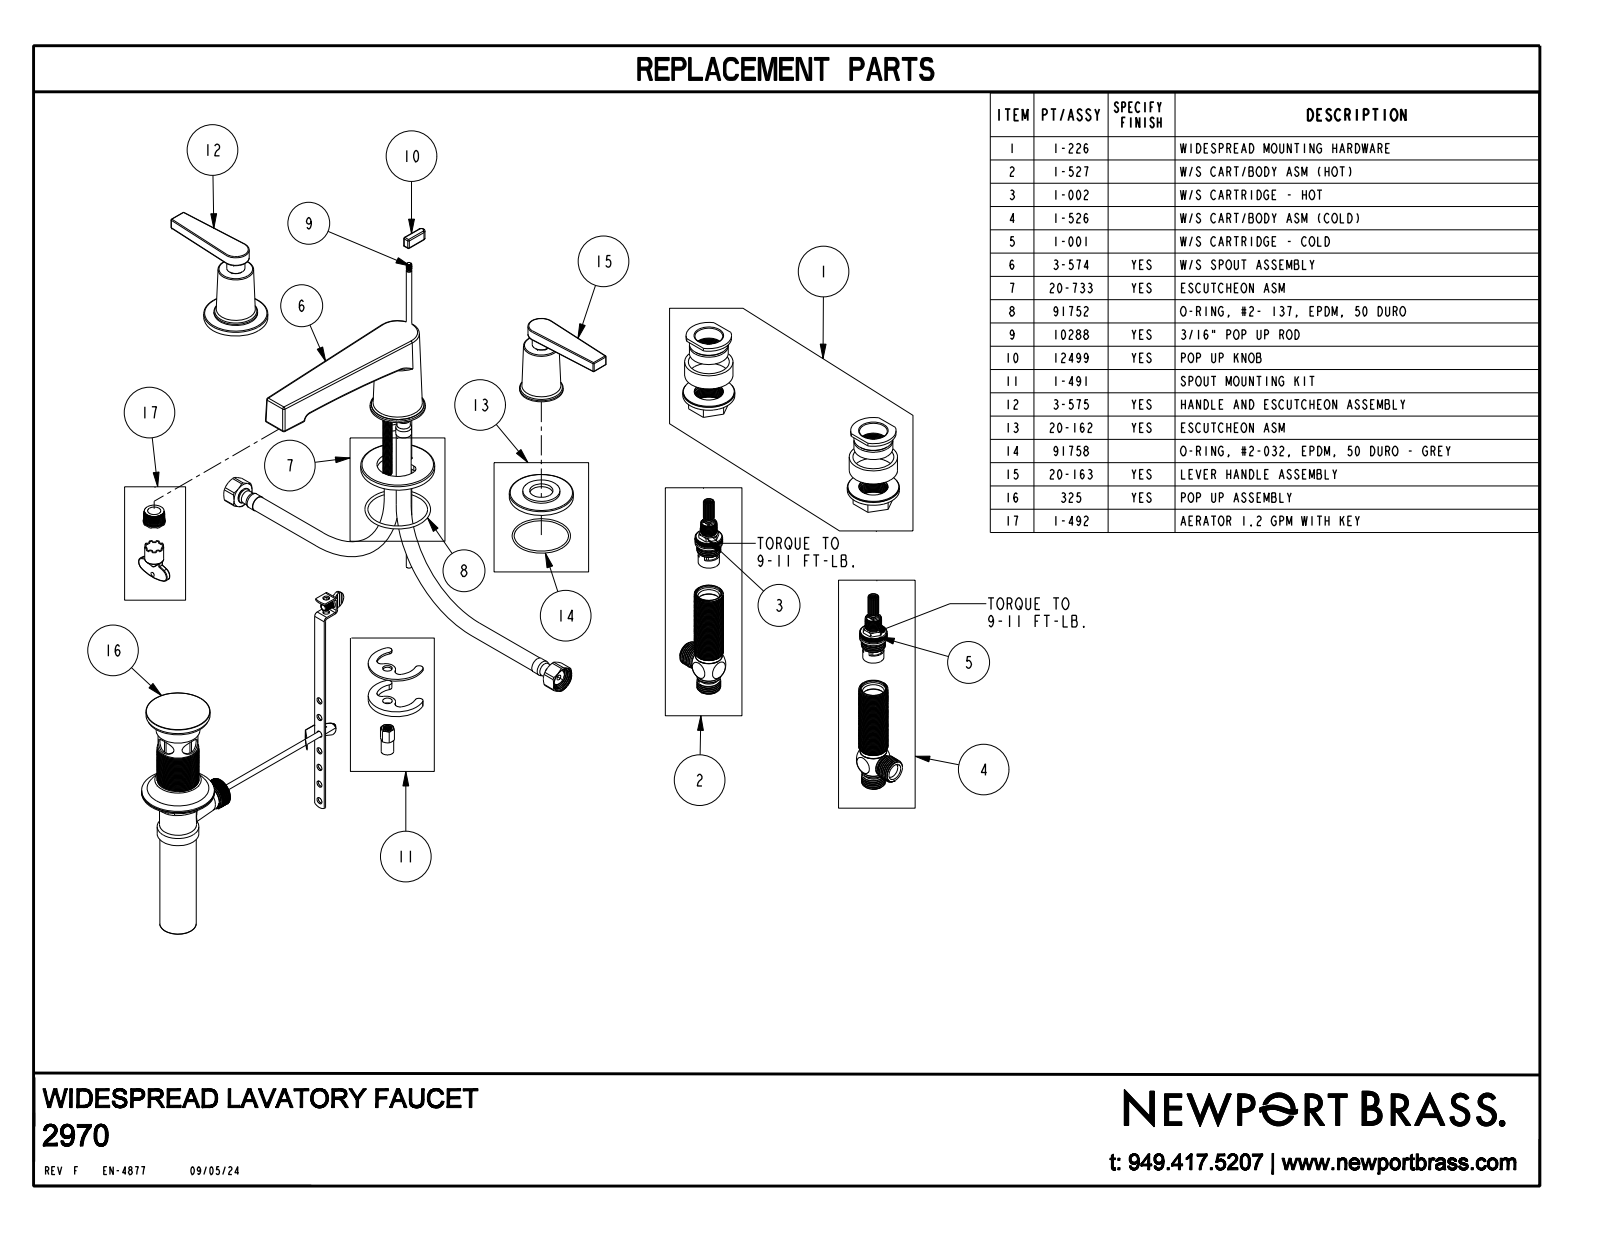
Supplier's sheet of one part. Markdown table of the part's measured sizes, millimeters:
| quantity | value |
| --- | --- |
| part name | 2970 |
| STEP written by | CREO PARAMETRIC BY PTC INC, 2018400 (CONFIG_CONTROL_DESIGN) |
| units | millimeters |
| bodies | 3 solids, 168 faces (37 planar, 67 cylindrical, 64 other) |
| overall size | 348 × 184.7 × 84.2 |
| volume | 340 400 mm³ |
| surface area | 65 610 mm² |
| round holes (diameter × count) | 33 × 2 |
| round bosses / shafts (diameter × count) | 55.9 × 2, 38.1 × 2, 32.4 × 2, 15.9 × 2, 13.3 × 2, 64.5 × 1 |
| partial cylindrical surfaces (radius × count) | 0.8 × 16, 1 × 10, 1.5 × 9, 11.7 × 2, 3.2 × 1, 4 × 1, 5.4 × 1, 889 × 1 |
| main face-to-face distances | 84.2, 4.7, 79.4, 72.9, 68.1, 11.3, 63.4, 58.6, 9.5, 20.8 |
| hole center spacings | 203.2 |
